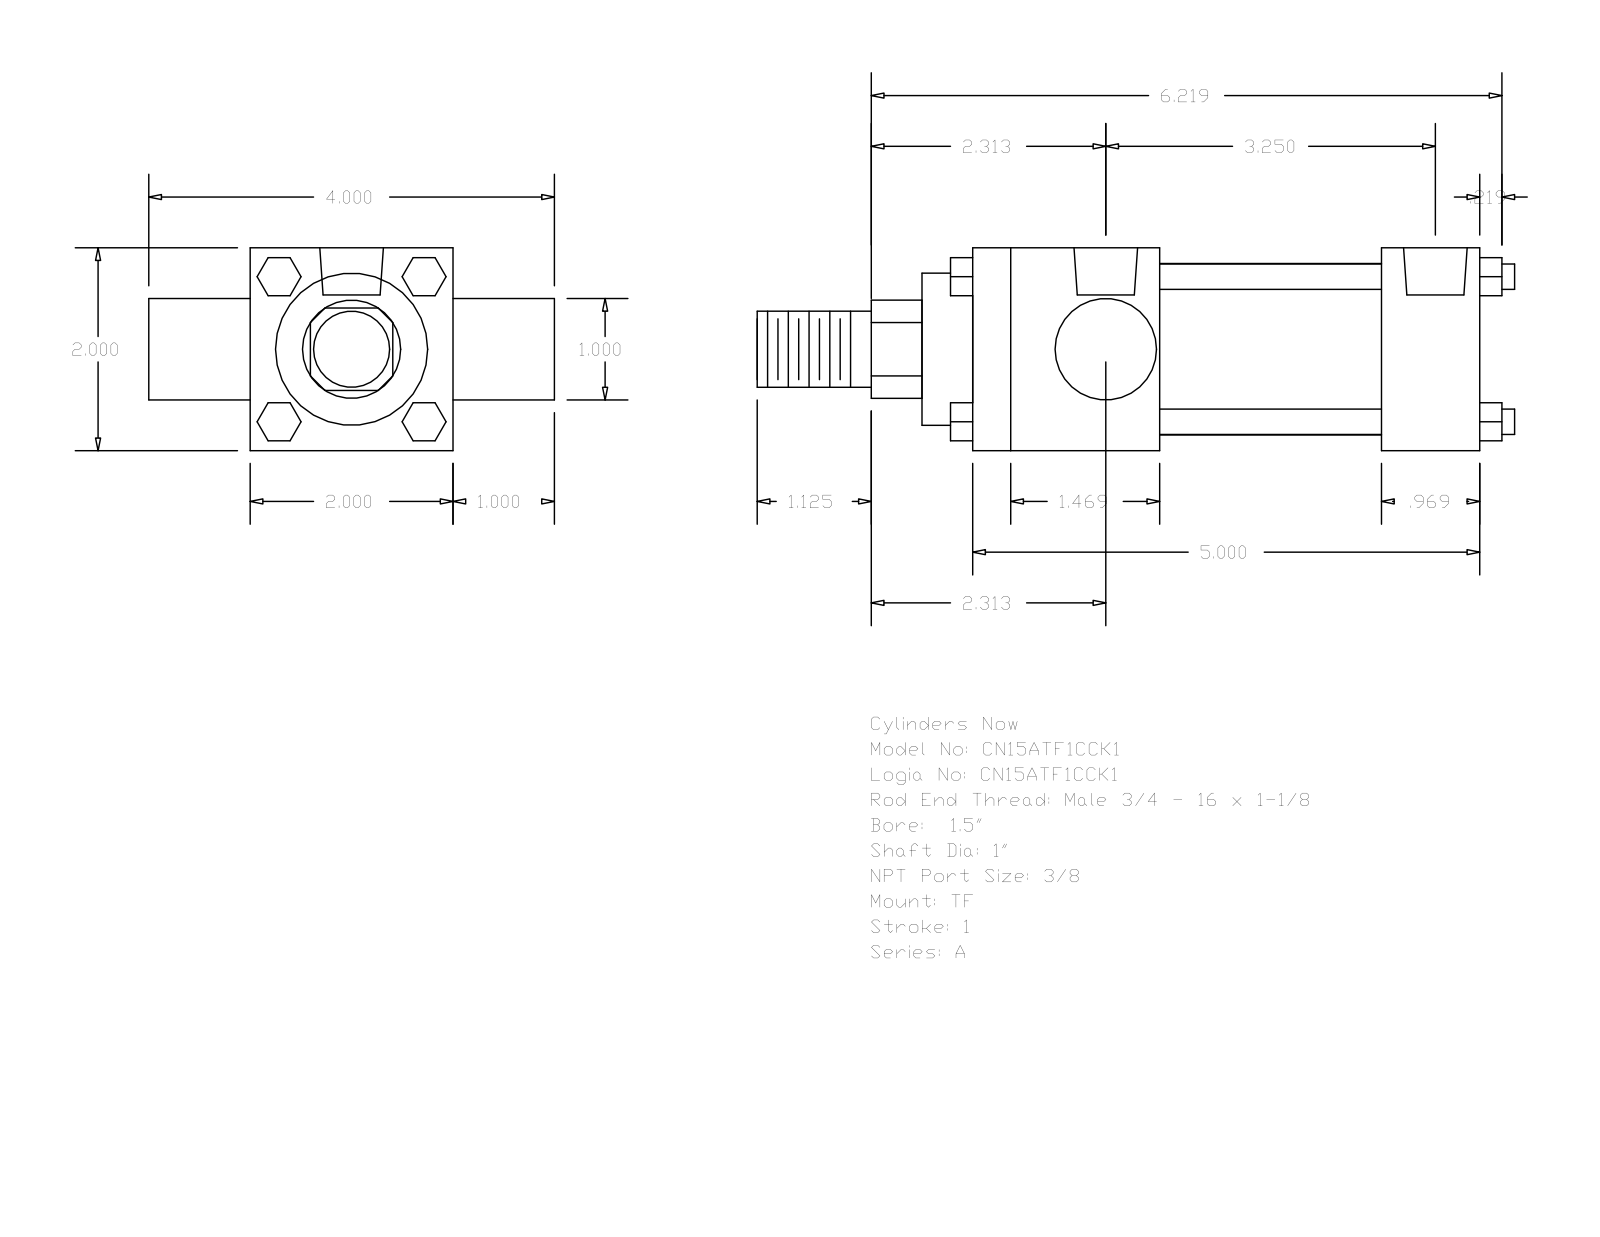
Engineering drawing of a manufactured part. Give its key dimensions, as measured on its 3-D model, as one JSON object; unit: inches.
{"part_name": "A_TF__0150_1", "step_written_by": "GSSL Pune (CONFIG_CONTROL_DESIGN)", "units": "inches", "bodies": {"solids": 0, "faces": 120, "planar": 92, "cylindrical": 28, "other": 0}, "overall_size": [7.469, 4, 2], "round_holes": [[0.219, 3], [0.627, 2]], "round_bosses_or_shafts": [[0.25, 4], [1, 2], [1.69, 1], [1.5, 1], [0.75, 1]], "partial_cylinders_radius": [[0.484, 1]], "face_to_face_distances": [2, 1, 5, 3, 1.844, 4.031, 2.187, 3.156, 0.969, 0.5], "hole_center_spacings": [0.156, 3.094, 2.937, 3.25]}
